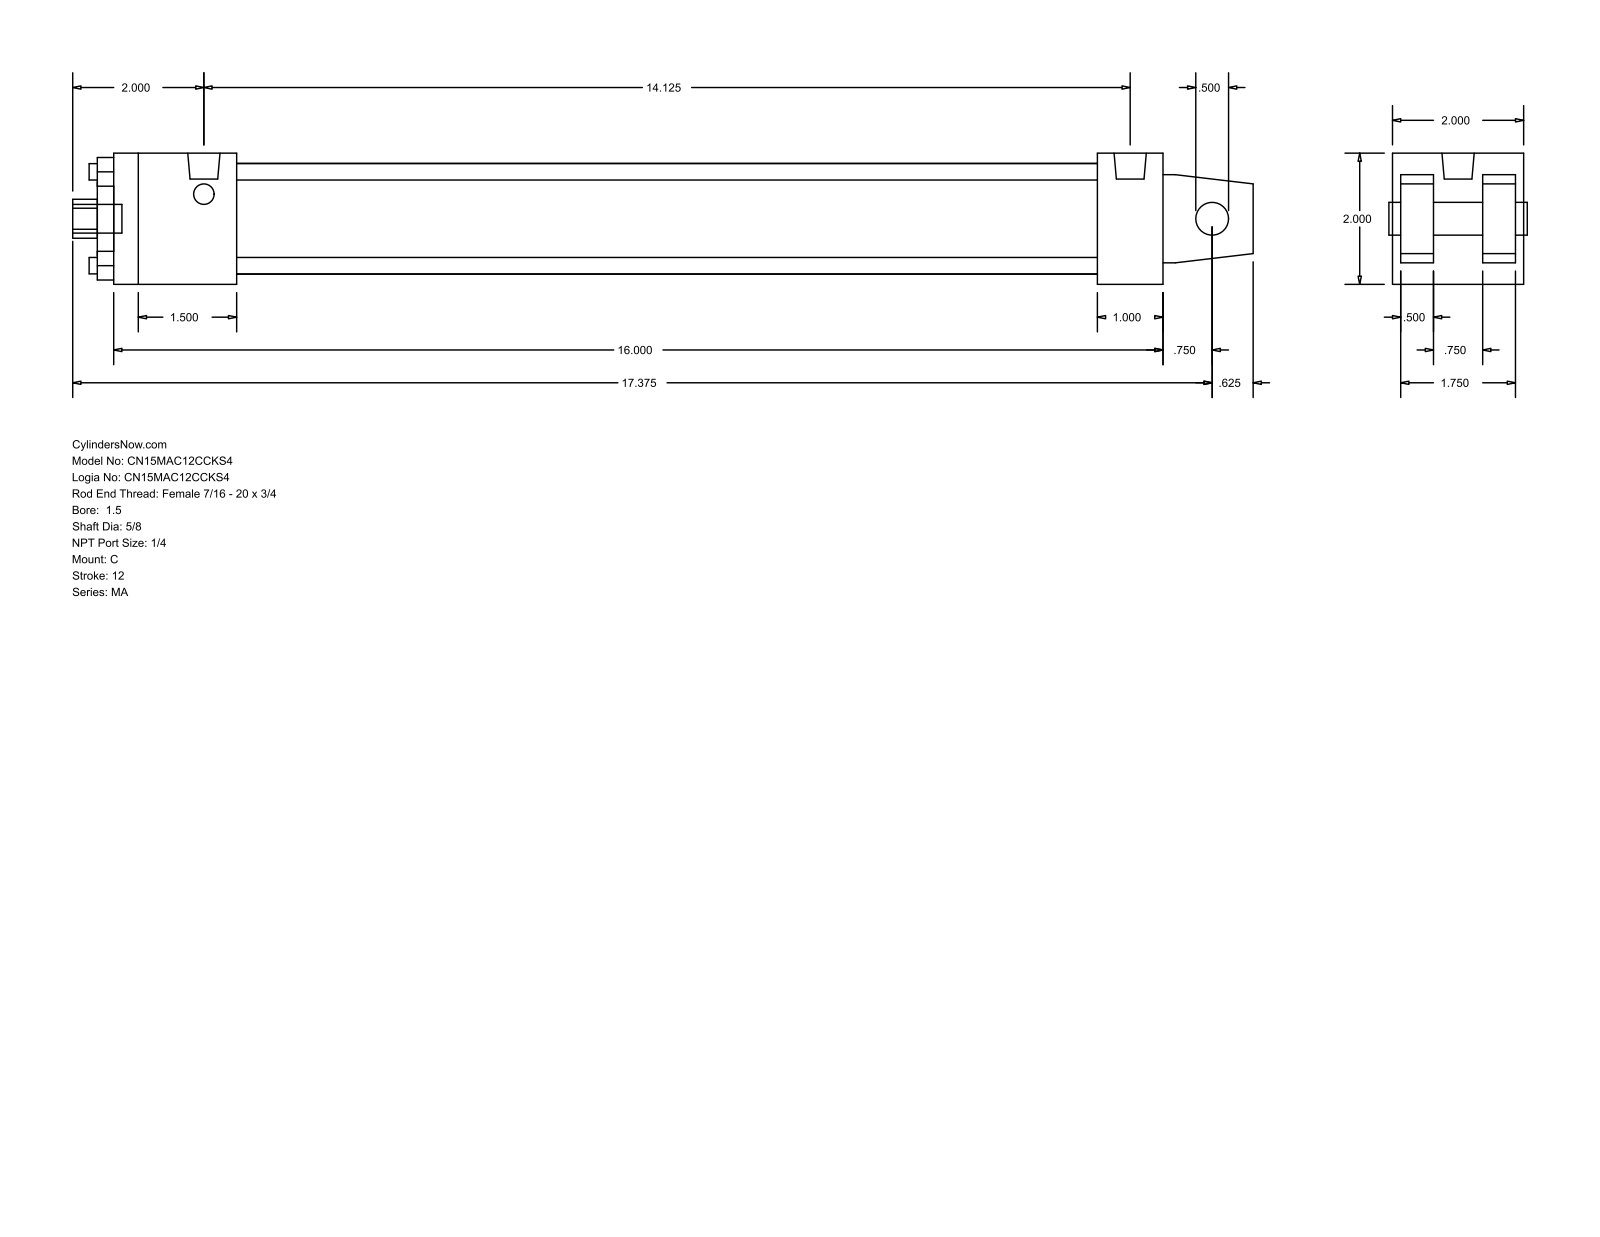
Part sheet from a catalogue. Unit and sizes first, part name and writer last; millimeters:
Units: millimetres
Overall size (bounding box): 457.2 × 50.8 × 50.8
Round holes (diameter × count): ⌀6.35 ×4, ⌀12.7 ×1, ⌀15.88 ×1, ⌀28.57 ×1, ⌀42.93 ×1
Round bosses / shafts (diameter × count): ⌀7.94 ×4, ⌀12.49 ×2, ⌀11.11 ×1
Partial cylindrical surfaces — rounded edges, fillets, slot ends (radius × count): R7.54 ×1
Main face-to-face distances: 50.8, 34.93, 12.7, 3.17, 15.87, 47.63, 31.76, 406.39, 381, 25.39
Hole centre spacings: 25.68, 36.32, 51.36
Bodies: 0 solids, 103 faces (76 planar, 27 cylindrical, 0 other)
Part name (STEP PRODUCT): MA_C__0150_0.625
STEP written by: GSSL Pune (CONFIG_CONTROL_DESIGN)
